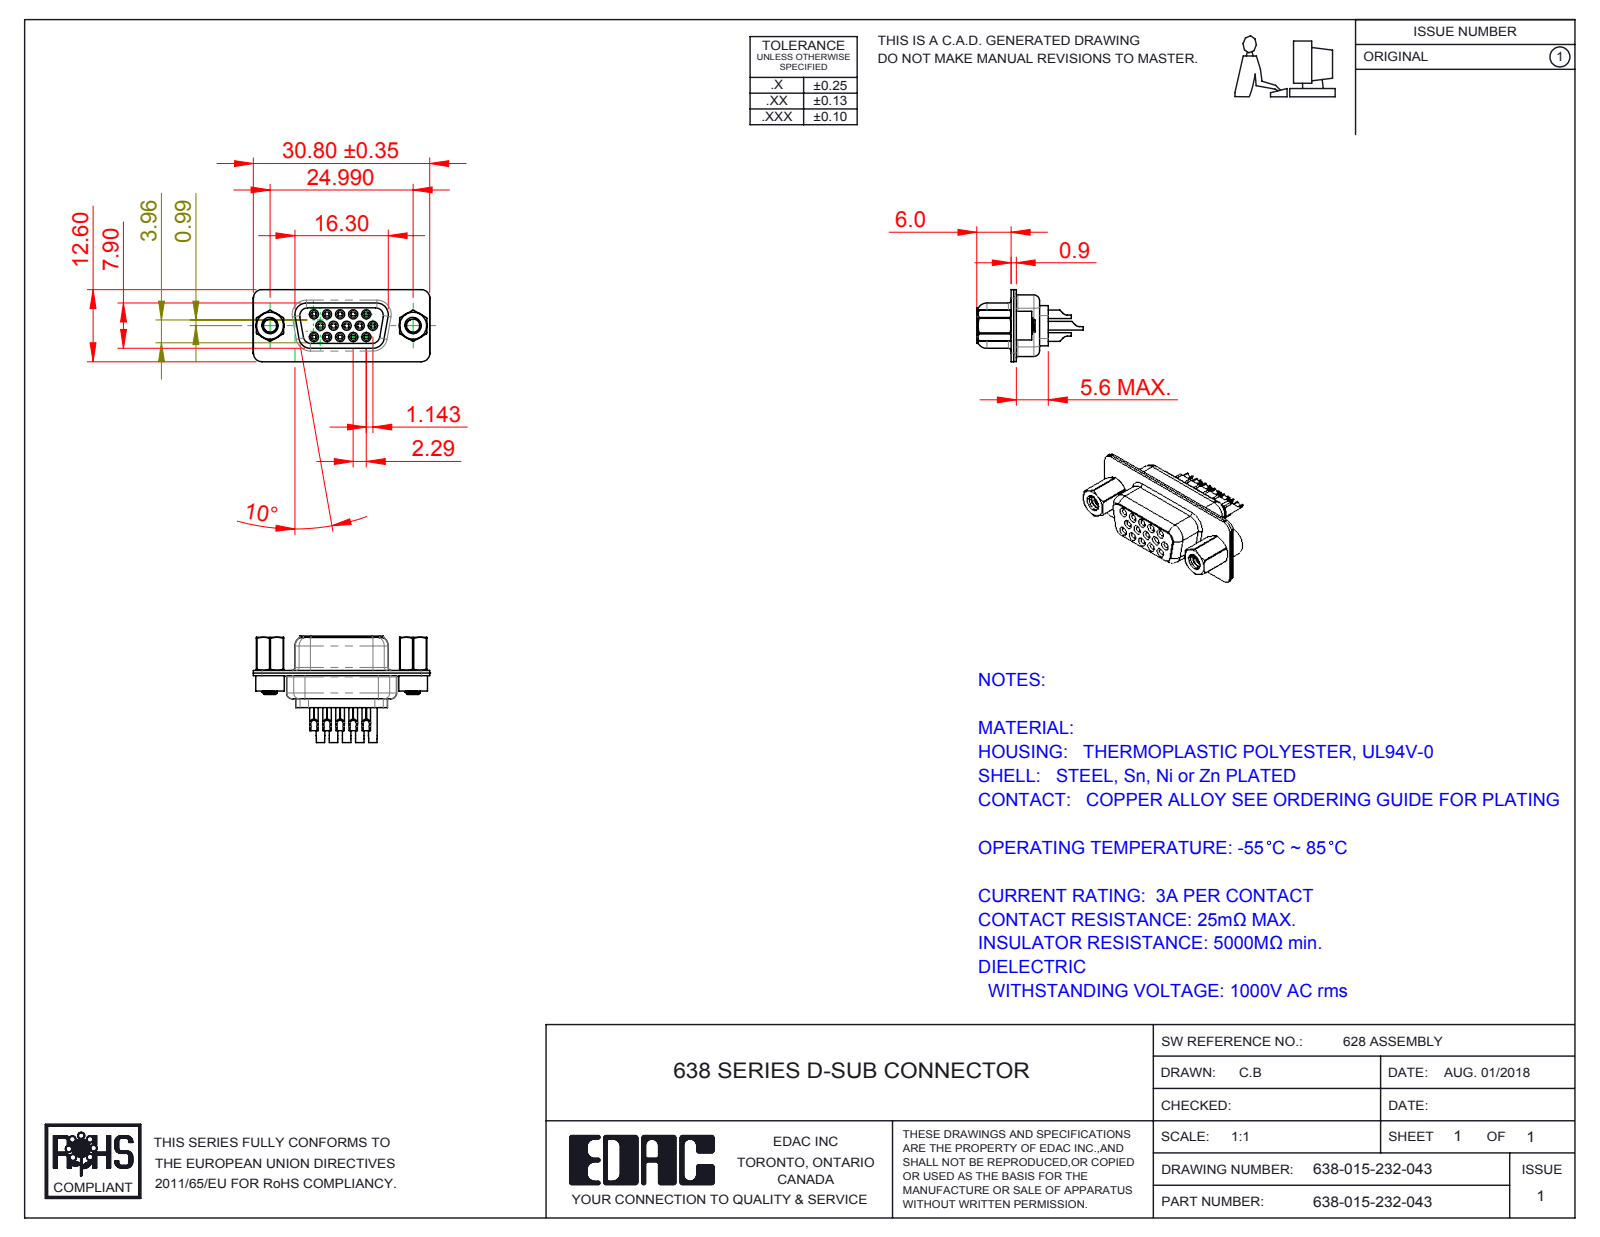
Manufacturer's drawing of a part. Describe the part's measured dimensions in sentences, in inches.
The part is named "638 Housing_15 Contacts; 638 Shell Front_15 Contacts; 638 Shell Rear_15 Contacts; 638 Contact Row 1_32L (+5 more)". Its 3-D file was written by "SolidWorks 2016 (CONFIG_CONTROL_DESIGN)". It is 22 solids with 1740 faces: 404 planar, 584 cylindrical and 752 other. Overall it measures 1.213 by 0.732 by 0.496 inches. Its volume is 0.111 cubic inches and its surface area 9.833 square inches. Round holes: 15 of diameter 0.031, 15 of diameter 0.039, 15 of diameter 0.043, 15 of diameter 0.063, 15 of diameter 0.067, 15 of diameter 0.071, 2 of diameter 0.079, 2 of diameter 0.089, 2 of diameter 0.09, 2 of diameter 0.157, 2 of diameter 0.159, 2 of diameter 0.191. Round bosses or shafts: 15 of diameter 0.079, 15 of diameter 0.059, 15 of diameter 0.047, 2 of diameter 0.197, 2 of diameter 0.195, 2 of diameter 0.189, 2 of diameter 0.11. Partial cylindrical surfaces (rounded edges, fillets, slot ends): 20 of radius 0.059, 12 of radius 0.079, 10 of radius 0.011, 8 of radius 0.061, 7 of radius 0.039, 5 of radius 0.053, 4 of radius 0.01, 4 of radius 0.02. The main face-to-face distances are 0.018, 0.035, 0.016, 0.056, 0.35, 0.26, 0.055, 0.09, 0.244, 0.033. The hole center spacings are 0.156, 0.09, 0.18, 0.09, 0.238, 0.238, 0.27, 0.312.
